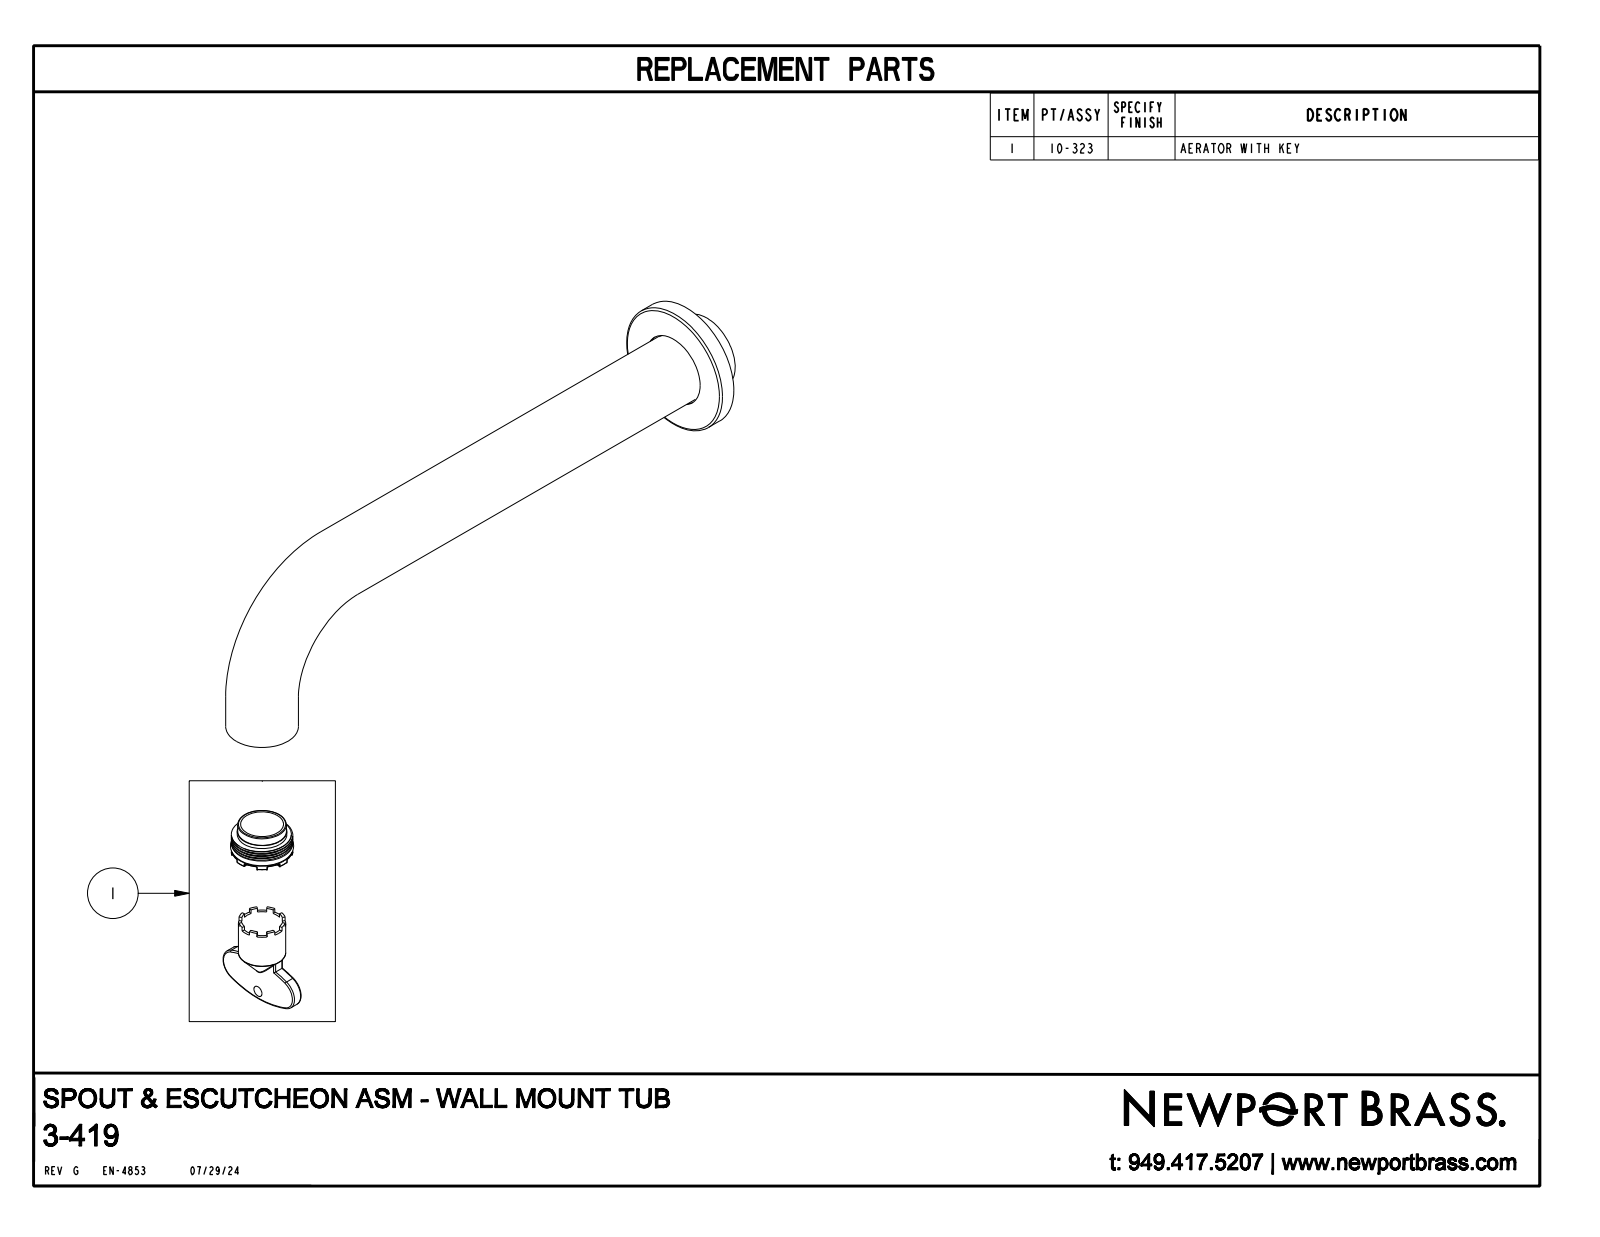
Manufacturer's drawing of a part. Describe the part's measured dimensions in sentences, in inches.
The part is named "3-419". Its 3-D file was written by "CREO PARAMETRIC BY PTC INC, 2018400 (AUTOMOTIVE_DESIGN)". It is 1 solid with 16 faces: 4 planar, 8 cylindrical and 4 other. Overall it measures 9.15 by 2.925 by 1.85 inches. Its volume is 8.399 cubic inches and its surface area 37.53 square inches. Round bosses or shafts: 2 of diameter 1, 1 of diameter 1.85, 1 of diameter 1.1. The main face-to-face distances are 0.25, 0.4, 0.65.
